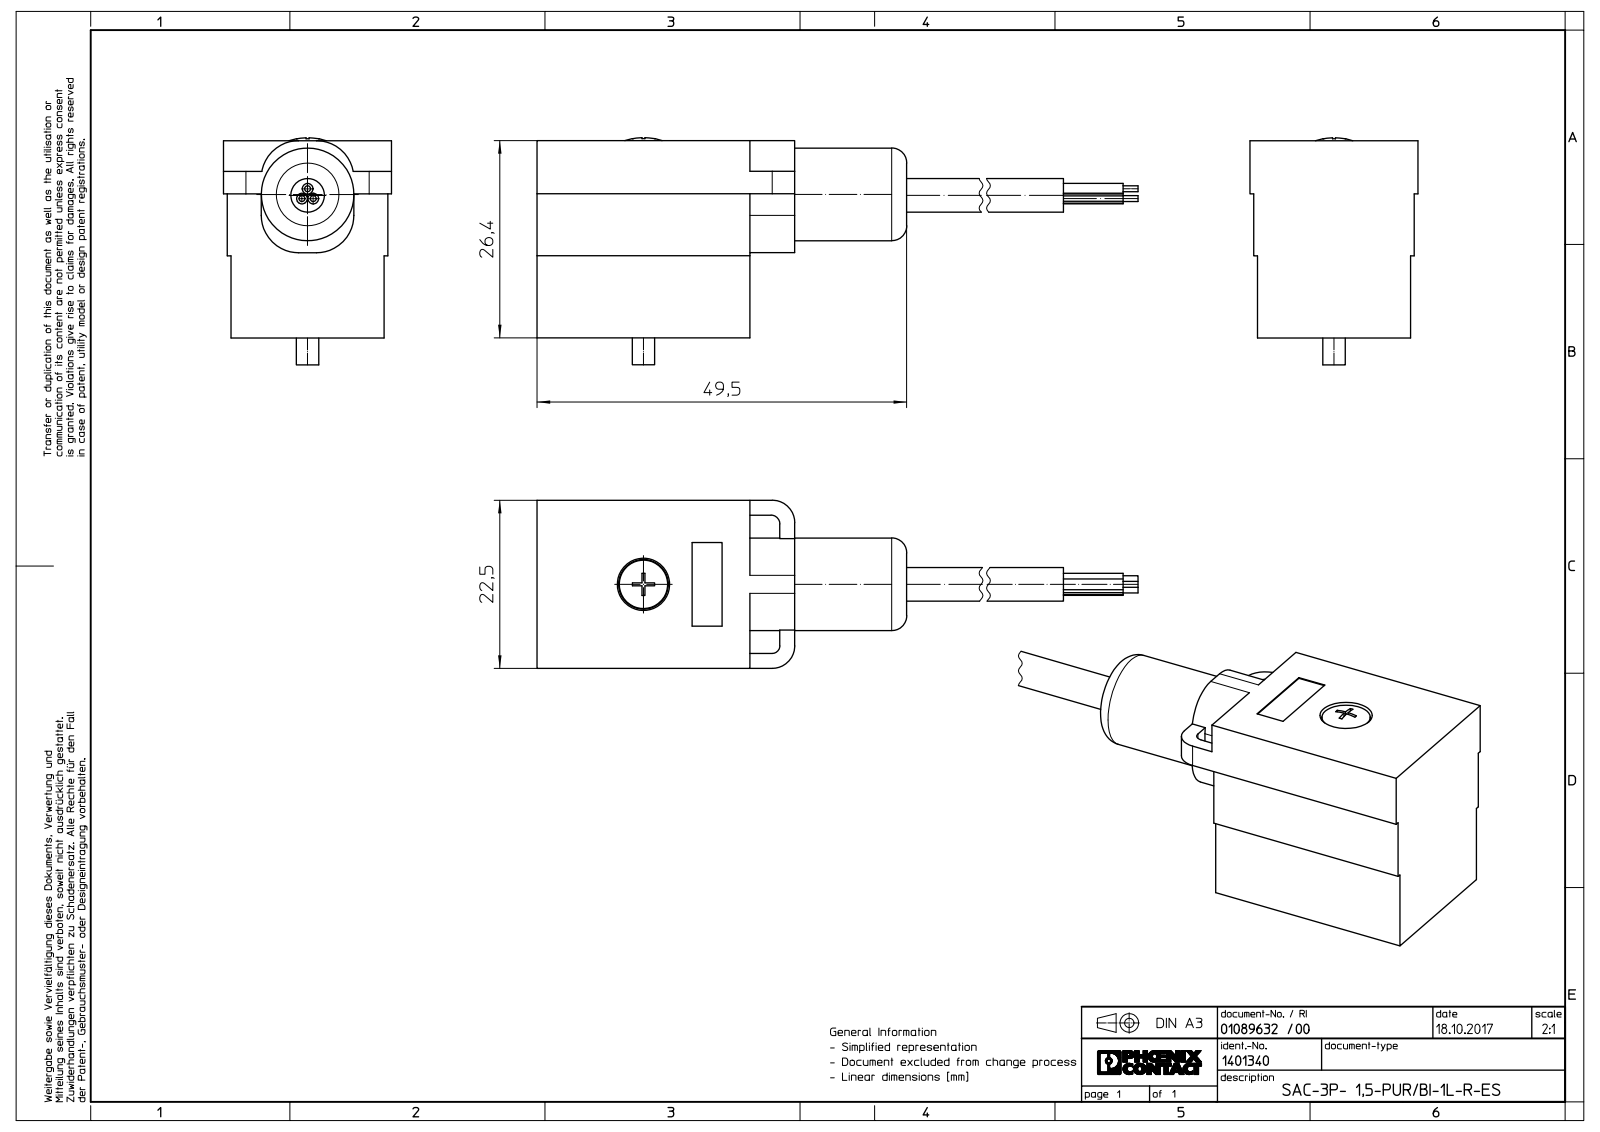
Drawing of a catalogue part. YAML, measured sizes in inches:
part_name: "5811-1 Actuator cable - SAC-3P- 1,5-PURBI-1L-R-ES - 1401340; 5811 Actuator cable - SAC-3P- 1,5-PURBI-1L-R-ES - 1401340"
step_written_by: "Alibre (AUTOMOTIVE_DESIGN)"
units: inches
bodies: {solids: 1, faces: 132, planar: 93, cylindrical: 33, other: 6}
overall_size: [6.28, 1.196, 0.886]
volume: 1.206
surface_area: 10.8
round_holes:
  - {diameter: 0.24, count: 1}
  - {diameter: 0.276, count: 1}
round_bosses_or_shafts:
  - {diameter: 0.031, count: 3}
  - {diameter: 0.056, count: 2}
  - {diameter: 0.488, count: 1}
  - {diameter: 0.177, count: 1}
  - {diameter: 0.118, count: 1}
partial_cylinders:
  - {radius: 0.197, count: 4}
  - {radius: 0.118, count: 2}
  - {radius: 0.028, count: 1}
  - {radius: 0.039, count: 1}
  - {radius: 0.046, count: 1}
face_to_face_distances: [0.02, 0.846, 0.827, 0.039, 0.866, 1.122, 0.98, 0.807, 0.886, 0.059]
